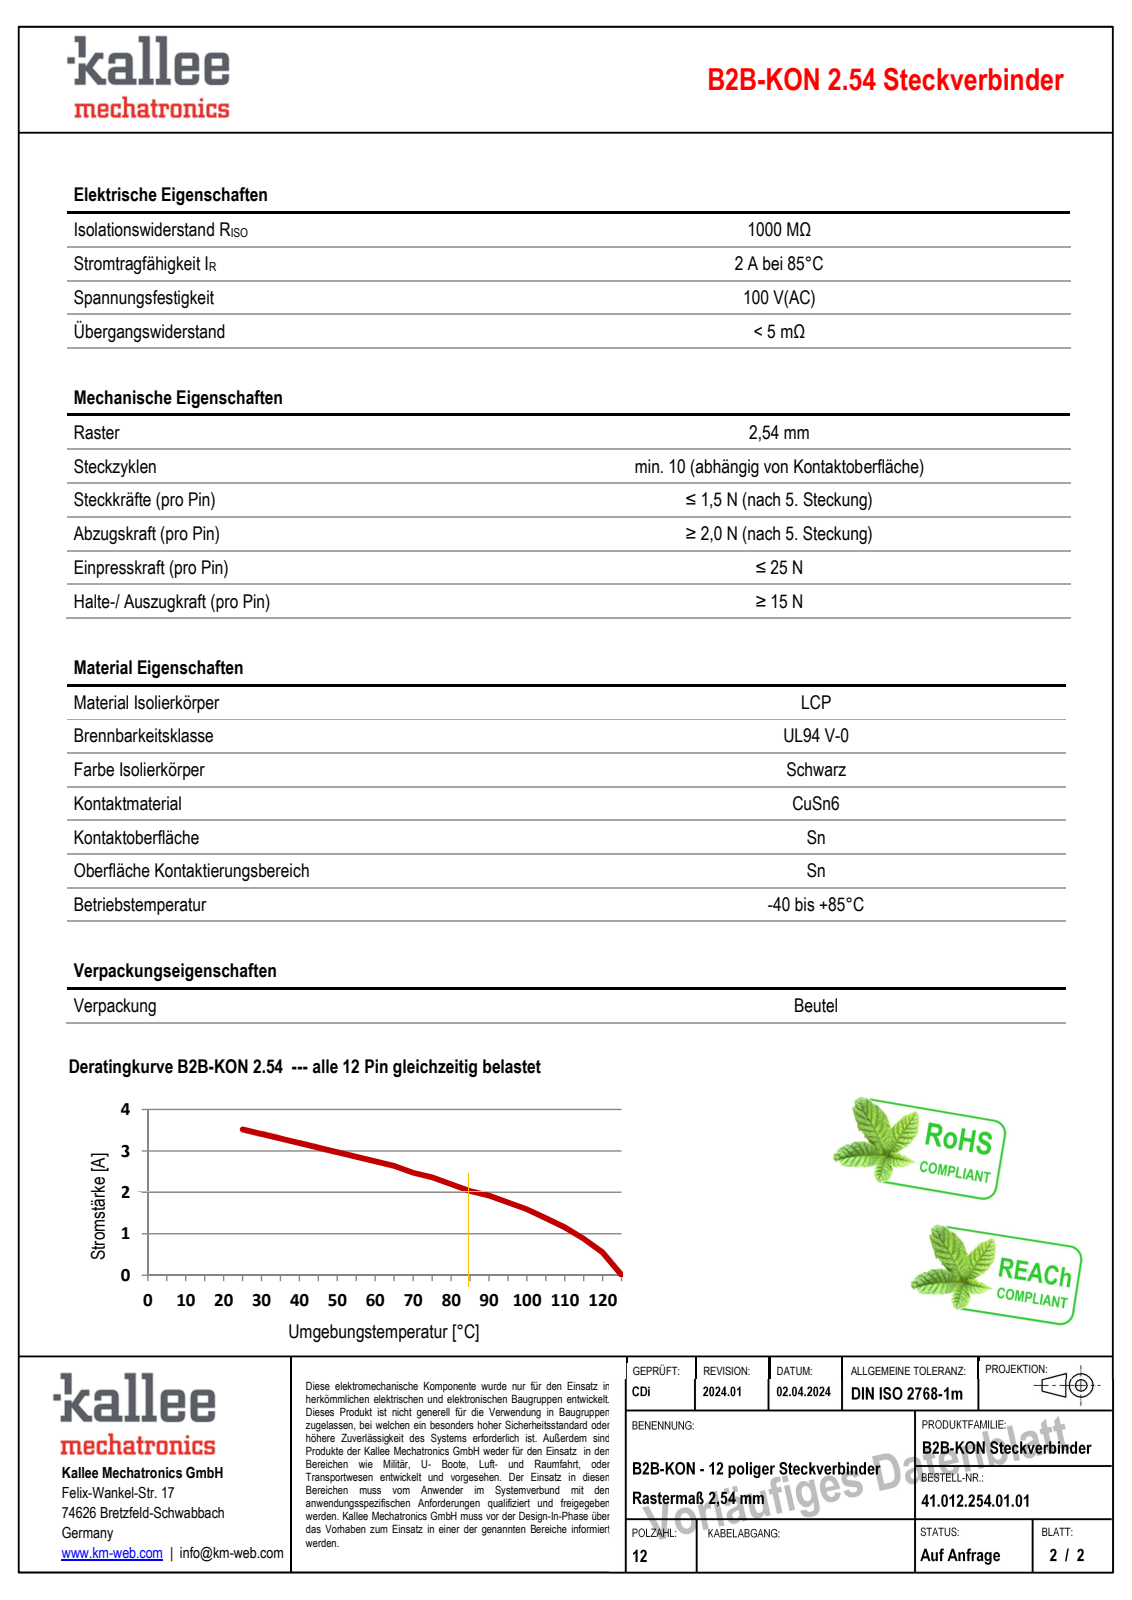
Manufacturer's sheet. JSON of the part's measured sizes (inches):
{"part_name": "B2B-KON_41.12.254.01.01 v2; B2B-KON_41.12.254.01.01; B2B-KON_41.12.254.01.01 (1)", "step_written_by": "Autodesk Translation Framework v12.20.1.177 (AUTOMOTIVE_DESIGN)", "units": "inches", "bodies": {"solids": 1, "faces": 619, "planar": 260, "cylindrical": 356, "other": 3}, "overall_size": [0.6, 0.591, 0.197], "volume_in3": 0.029, "surface_area_in2": 1.21, "round_holes": [[0.047, 5]], "partial_cylinders_radius": [[0.039, 60], [0.118, 42], [0.127, 24], [0.048, 12], [0.004, 6], [0.007, 6], [0.007, 6], [0.008, 6]], "face_to_face_distances": [0.02, 0.177, 0.1, 0.157, 0.276, 0.197, 0.016, 0.137, 0.056, 0.141], "hole_center_spacings": [0.1, 0.2, 0.3, 0.4]}
